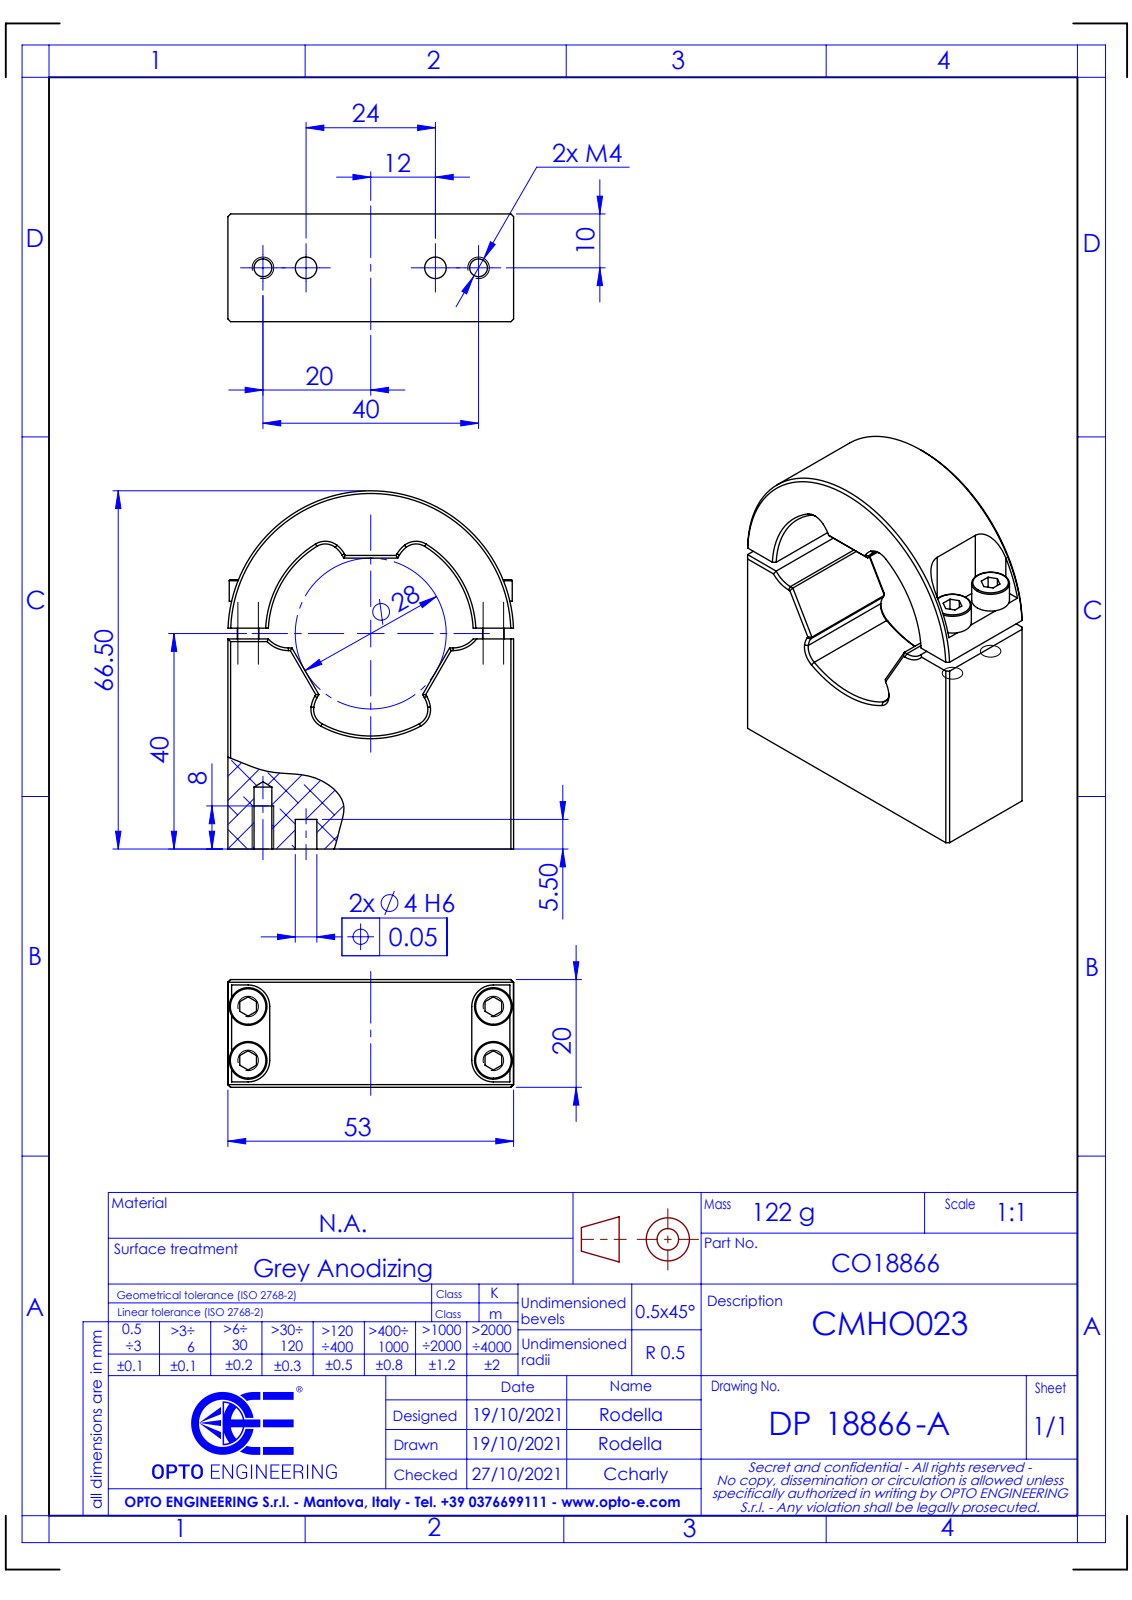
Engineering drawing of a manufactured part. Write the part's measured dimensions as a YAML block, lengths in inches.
part_name: "DP18866-A_CMHO023"
step_written_by: "SolidWorks 2021 (CONFIG_CONTROL_DESIGN)"
units: inches
bodies: {solids: 0, faces: 161, planar: 80, cylindrical: 43, other: 38}
overall_size: [2.618, 2.087, 0.787]
round_holes:
  - {diameter: 0.13, count: 2}
  - {diameter: 0.157, count: 2}
round_bosses_or_shafts:
  - {diameter: 0.276, count: 4}
  - {diameter: 0.157, count: 4}
partial_cylinders:
  - {radius: 0.197, count: 6}
  - {radius: 0.118, count: 4}
  - {radius: 0.157, count: 4}
  - {radius: 0.749, count: 1}
  - {radius: 1.043, count: 1}
face_to_face_distances: [0.787, 2.087, 1.811, 1.535, 0.276, 0.306, 1.781, 1.614, 0.079, 0.197]
hole_center_spacings: [0.315, 1.26, 0.945, 1.575]
